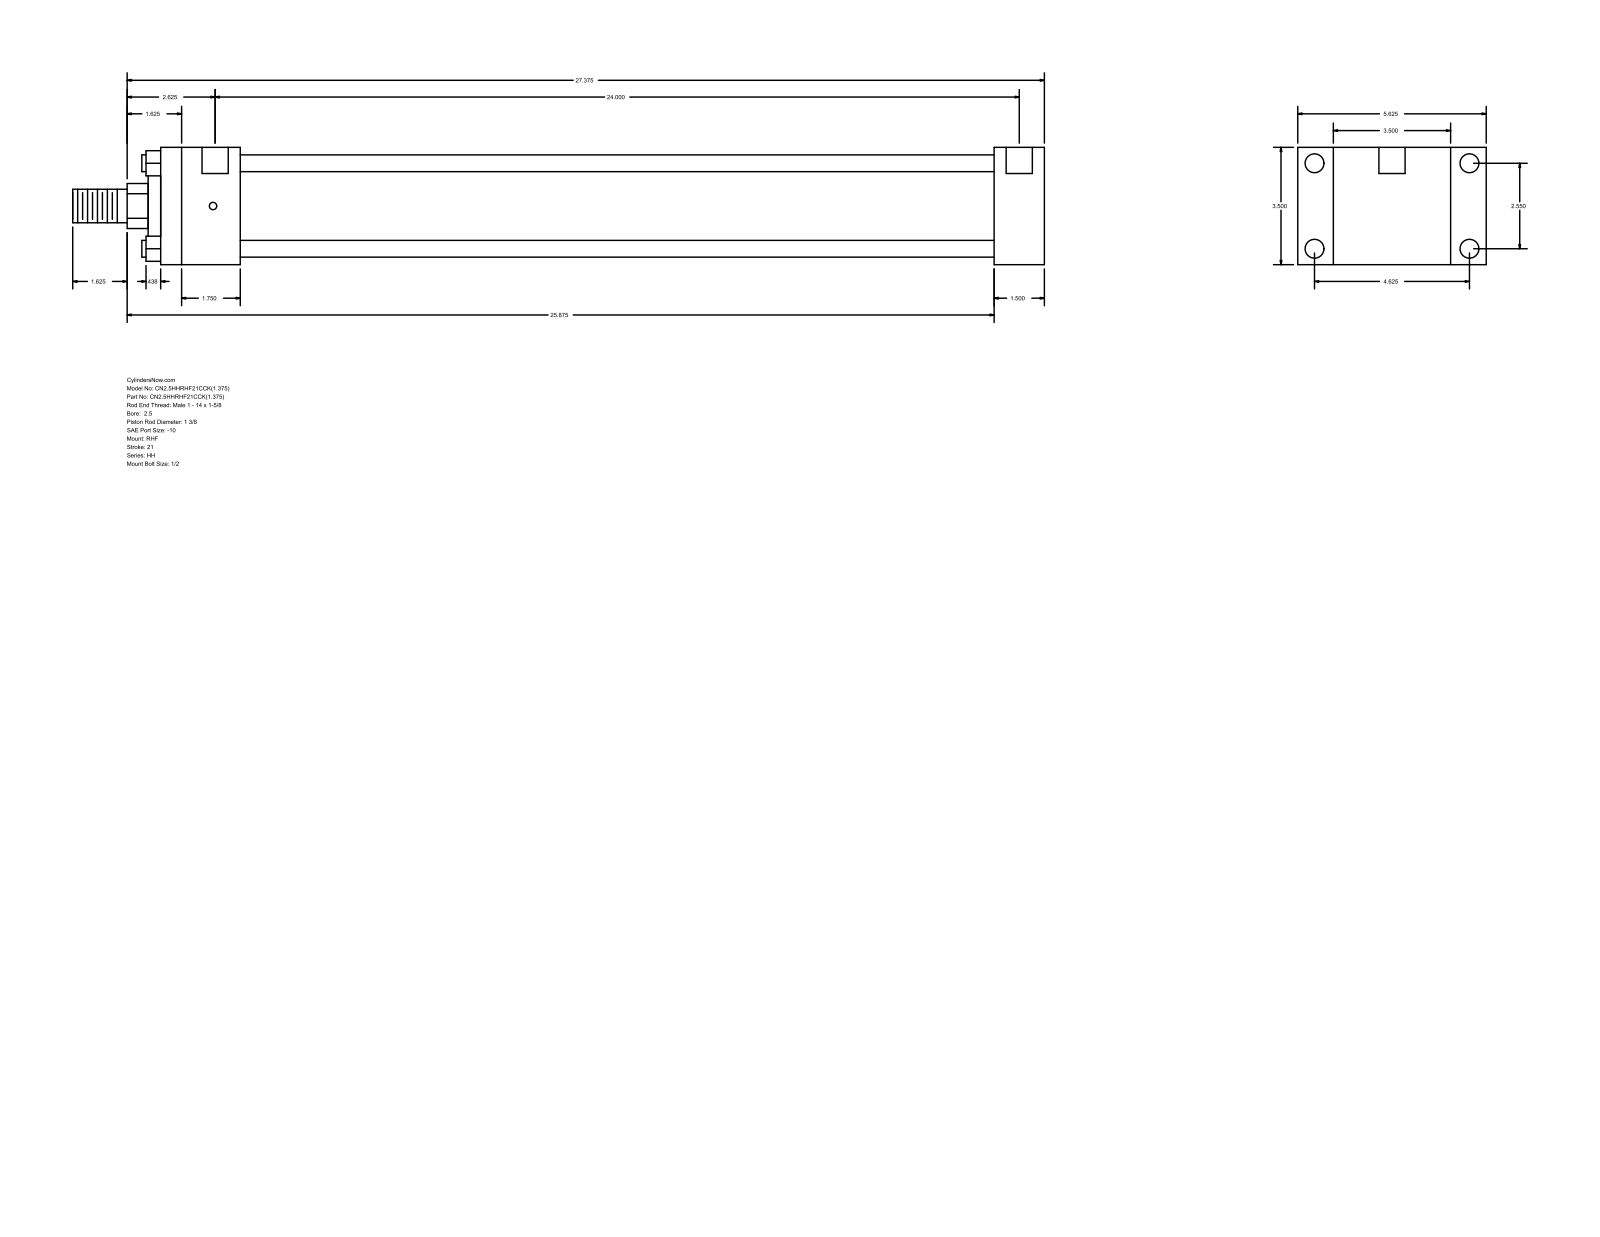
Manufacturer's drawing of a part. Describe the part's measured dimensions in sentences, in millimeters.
The part is named "HH_RHF__0250_1.375". Its 3-D file was written by "GSSL Pune (CONFIG_CONTROL_DESIGN)". It is 0 solids with 88 faces: 60 planar, 28 cylindrical and 0 other. Overall it measures 736.6 by 142.88 by 88.9 millimeters. Round holes: 4 of diameter 5.56, 4 of diameter 14.3, 2 of diameter 19.84. Round bosses or shafts: 4 of diameter 12.7, 1 of diameter 73.03, 1 of diameter 50.8, 1 of diameter 34.92, 1 of diameter 25.4. Partial cylindrical surfaces (rounded edges, fillets, slot ends): 1 of radius 17.06. The main face-to-face distances are 88.9, 38.1, 26.99, 115.89, 631.83, 669.93, 142.88, 60.32, 571.51, 609.61. The hole center spacings are 64.76, 117.48, 134.15, 612.77, 1.58, 1.59, 609.6, 611.18.
